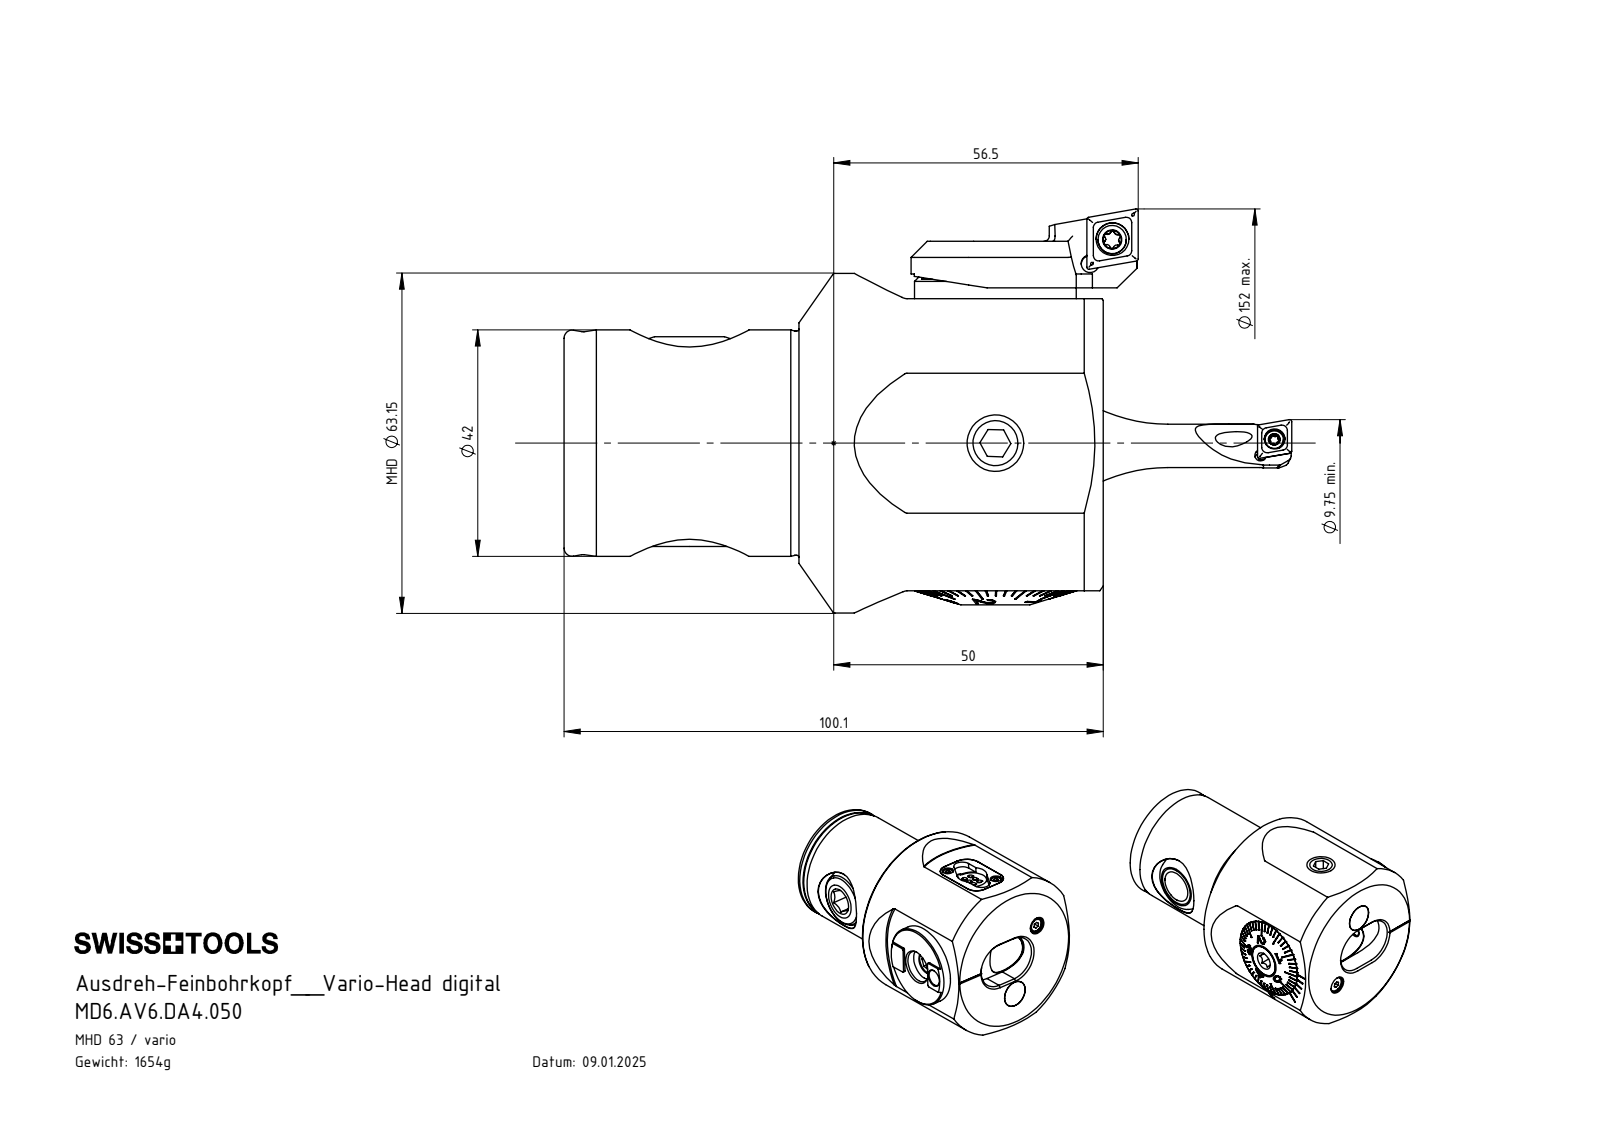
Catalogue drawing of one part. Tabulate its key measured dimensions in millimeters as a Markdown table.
| quantity | value |
| --- | --- |
| part name | MD6-ER1.022.040_A; ISO 4026 - M5 x 16; ISO 4762 - M2 x 4; PEF-DA3.010.032_A_F0U (+8 more) |
| STEP written by | SolidWorks 2017 (AUTOMOTIVE_DESIGN) |
| units | millimeters |
| bodies | 38 solids, 1182 faces (533 planar, 248 cylindrical, 401 other) |
| overall size | 100.08 × 63 × 63 |
| volume | 197 099 mm³ |
| surface area | 59 860 mm² |
| round holes (diameter × count) | 4.2 × 3, 8.5 × 3, 1.6 × 2, 2.2 × 2, 3.3 × 2, 6 × 2, 8 × 2, 12 × 2, 12.5 × 2, 1 × 1, 2.5 × 1, 5 × 1 |
| round bosses / shafts (diameter × count) | 1.9 × 6, 10 × 2, 3.8 × 2, 2 × 2, 63 × 1, 42 × 1, 41.6 × 1, 30 × 1 |
| partial cylindrical surfaces (radius × count) | 0.5 × 9, 1.1 × 6, 1.2 × 6, 0.8 × 4, 1.4 × 4, 1.9 × 4, 3.2 × 3, 4.4 × 3 |
| main face-to-face distances | 100.08, 2.5, 57.7, 5.3, 47.7, 53, 6.5, 33.65, 37.2, 32.45 |
| hole center spacings | 9.52, 0.5, 3, 8.43, 10.5, 11.32, 14.5, 14.51 |
